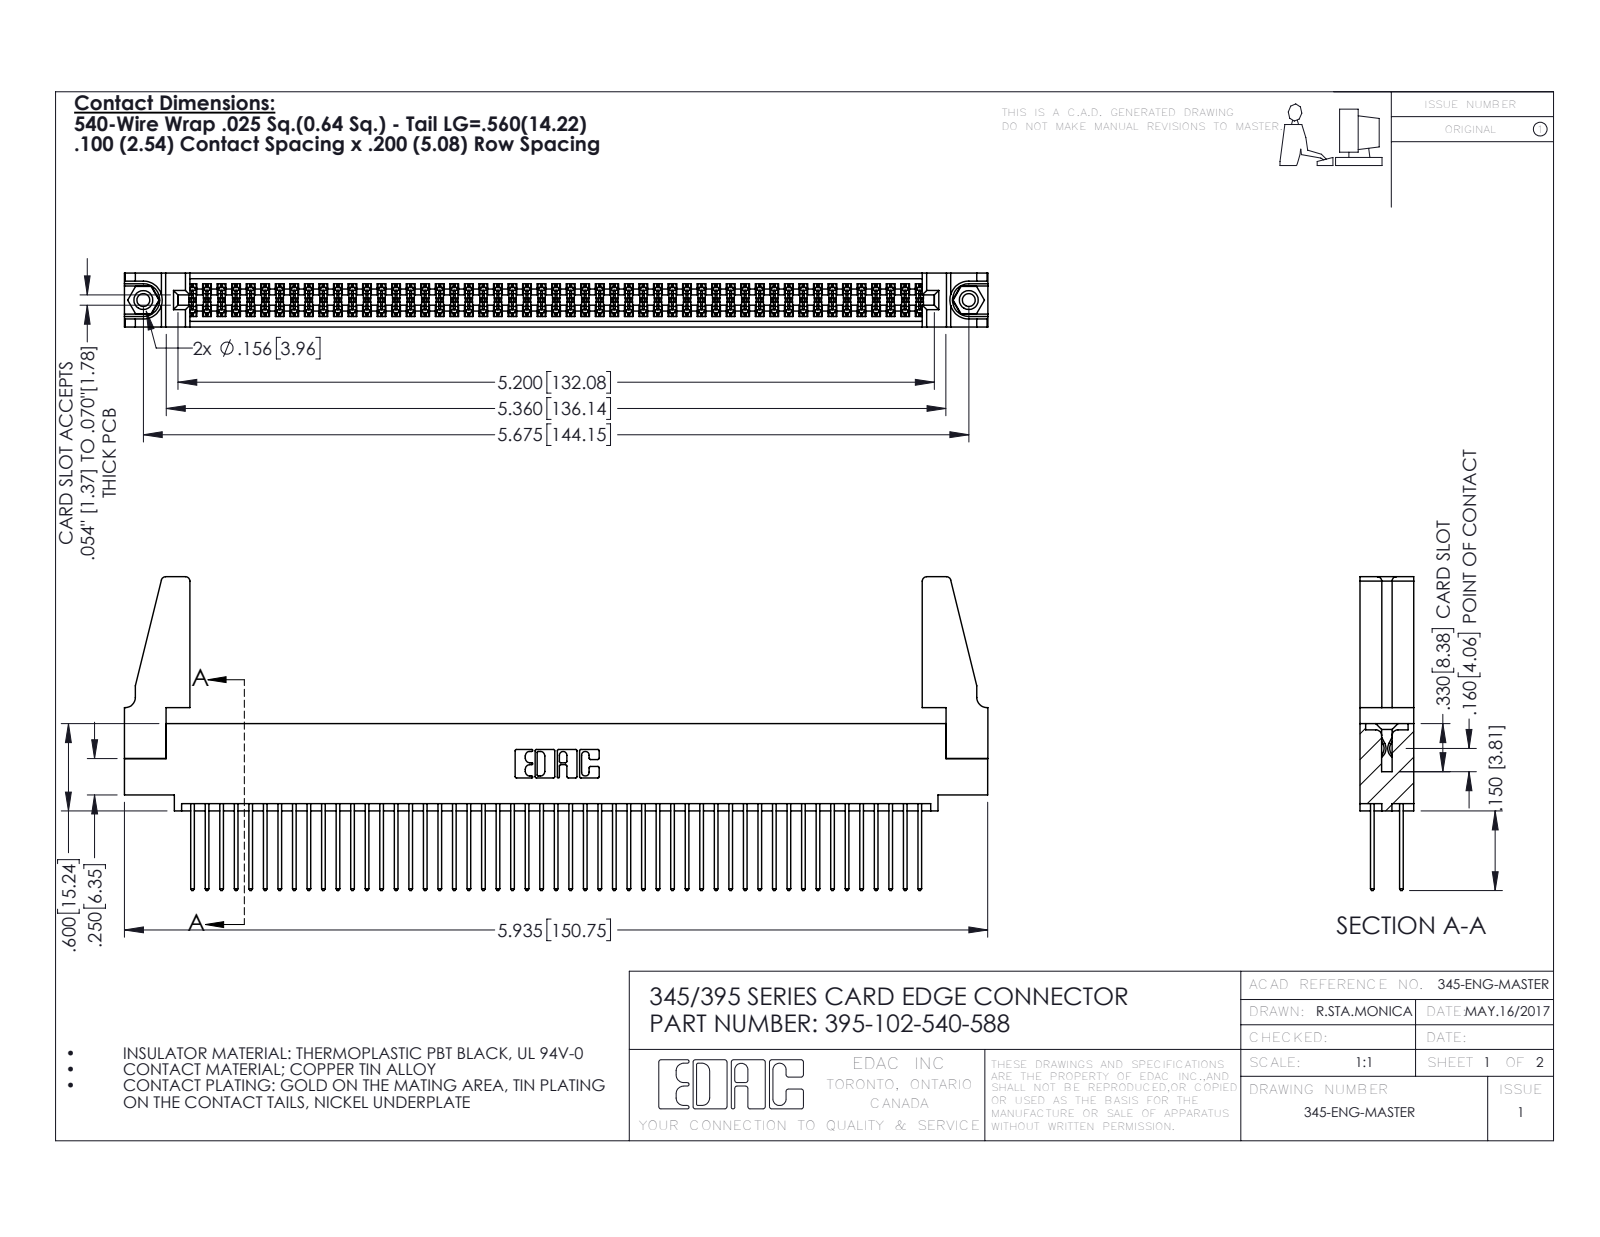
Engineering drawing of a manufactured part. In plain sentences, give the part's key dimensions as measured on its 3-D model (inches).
The part is named "345-292-001_345-293-140; 345 Part_0.110 Offset - 0.156 Dia-TH; 345-250-001_345-250-001-102; 395-102-540-588 (+1 more)". Its 3-D file was written by "SolidWorks 2016 (CONFIG_CONTROL_DESIGN)". It is 107 solids with 5354 faces: 3522 planar, 1816 cylindrical and 16 other. Overall it measures 5.936 by 2.157 by 0.37 inches. Its volume is 1.116 cubic inches and its surface area 42.5 square inches. Round holes: 2 of diameter 0.089, 2 of diameter 0.125, 2 of diameter 0.156, 1 of diameter 0.064. Round bosses or shafts: 2 of diameter 0.155. Partial cylindrical surfaces (rounded edges, fillets, slot ends): 153 of radius 0.006, 102 of radius 0.01, 22 of radius 0.01, 8 of radius 0.03, 6 of radius 0.007, 6 of radius 0.031, 3 of radius 0.026, 2 of radius 0.014. The main face-to-face distances are 0.072, 0.298, 0.2, 0.098, 0.272, 0.025, 0.37, 0.225, 0.175, 0.149. The hole center spacings are 0.27, 5.439, 5.675.
